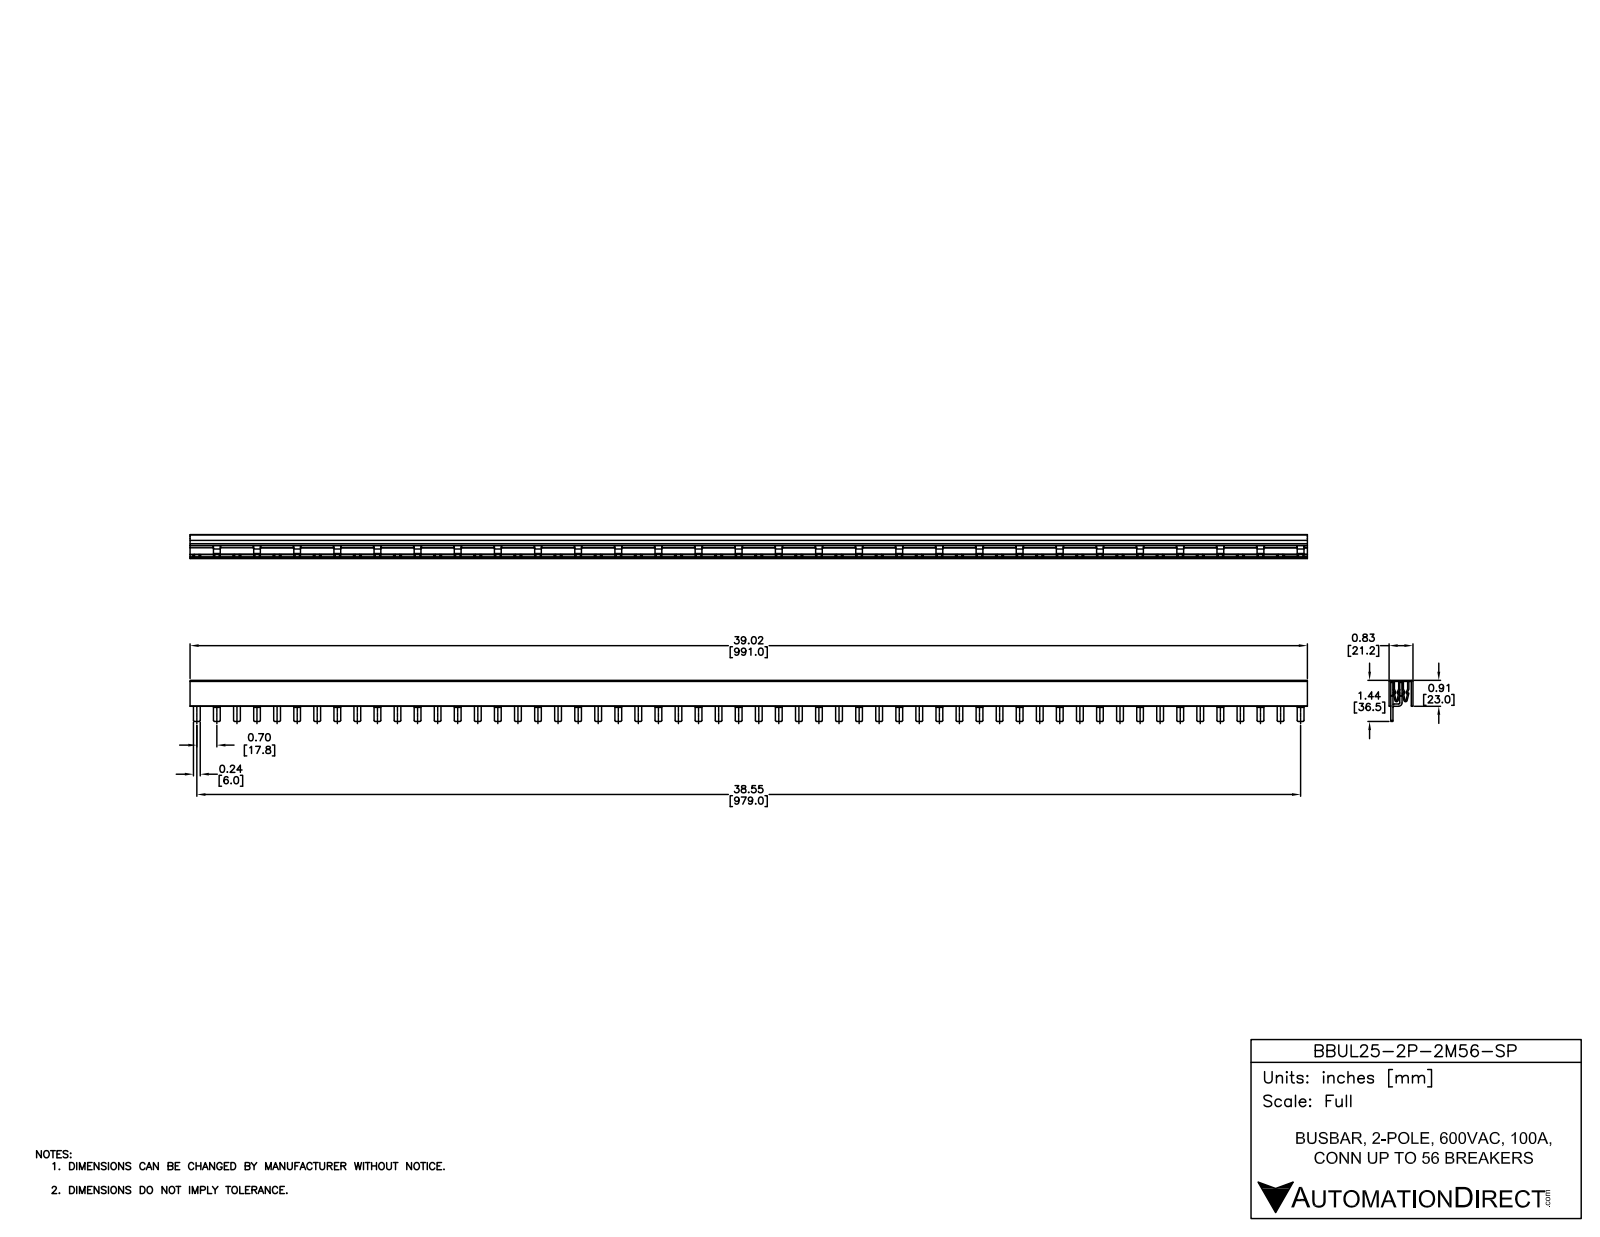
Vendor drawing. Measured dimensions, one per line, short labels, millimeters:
name: BBUL25-2P-2M56-SP
written by: SolidWorks 2014 (AUTOMOTIVE_DESIGN)
unit: mm
bodies: 1 solid, 458 faces (286 planar, 172 cylindrical, 0 other)
size: 991 × 36.5 × 21.2
volume: 491 798 mm³; area: 99 393 mm²
rounds: 115× R1, 2× R0.3, 1× R3
face distances: 21.2, 23, 3.5, 17.7, 1.5, 2, 19.7, 991, 36.5, 13.5
